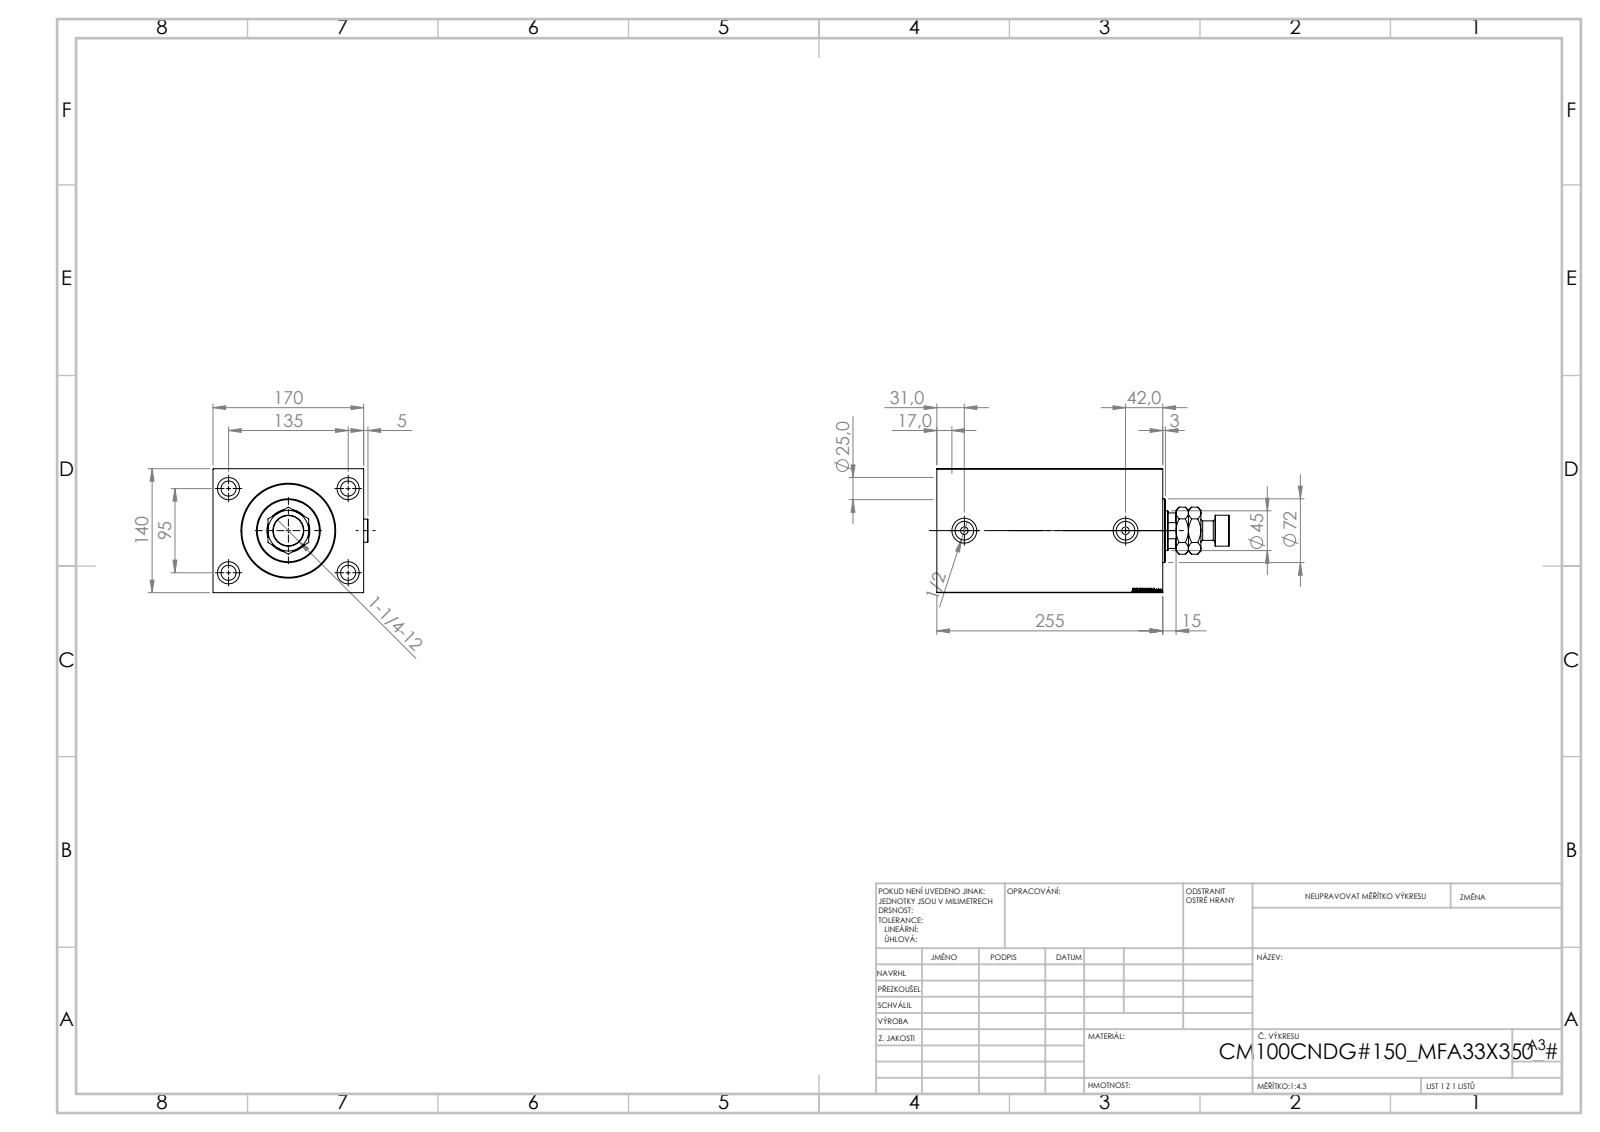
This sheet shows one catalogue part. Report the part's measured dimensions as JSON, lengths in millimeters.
{"part_name": "MFA; V450CM_C_Body; V450CM_C_VCP; Zatka_OIL_PORT (+1 more)", "step_written_by": "SolidWorks 2019 (CONFIG_CONTROL_DESIGN)", "units": "millimeters", "bodies": {"solids": 6, "faces": 971, "planar": 459, "cylindrical": 82, "other": 430}, "overall_size": [330, 174.9, 140], "volume_mm3": 4913000, "surface_area_mm2": 440885, "round_holes": [[17, 4], [25, 4], [8.5, 2], [20.96, 2], [28, 2], [31.5, 1], [45, 1], [48.5, 1], [100, 1], [102, 1], [105, 1]], "round_bosses_or_shafts": [[26, 2], [72, 1], [35, 1], [22, 1]], "partial_cylinders_radius": [[22, 1]], "face_to_face_distances": [140, 170, 255, 229, 26, 15, 240, 90, 214, 64], "hole_center_spacings": [82.54, 95, 135, 165.08, 182]}
